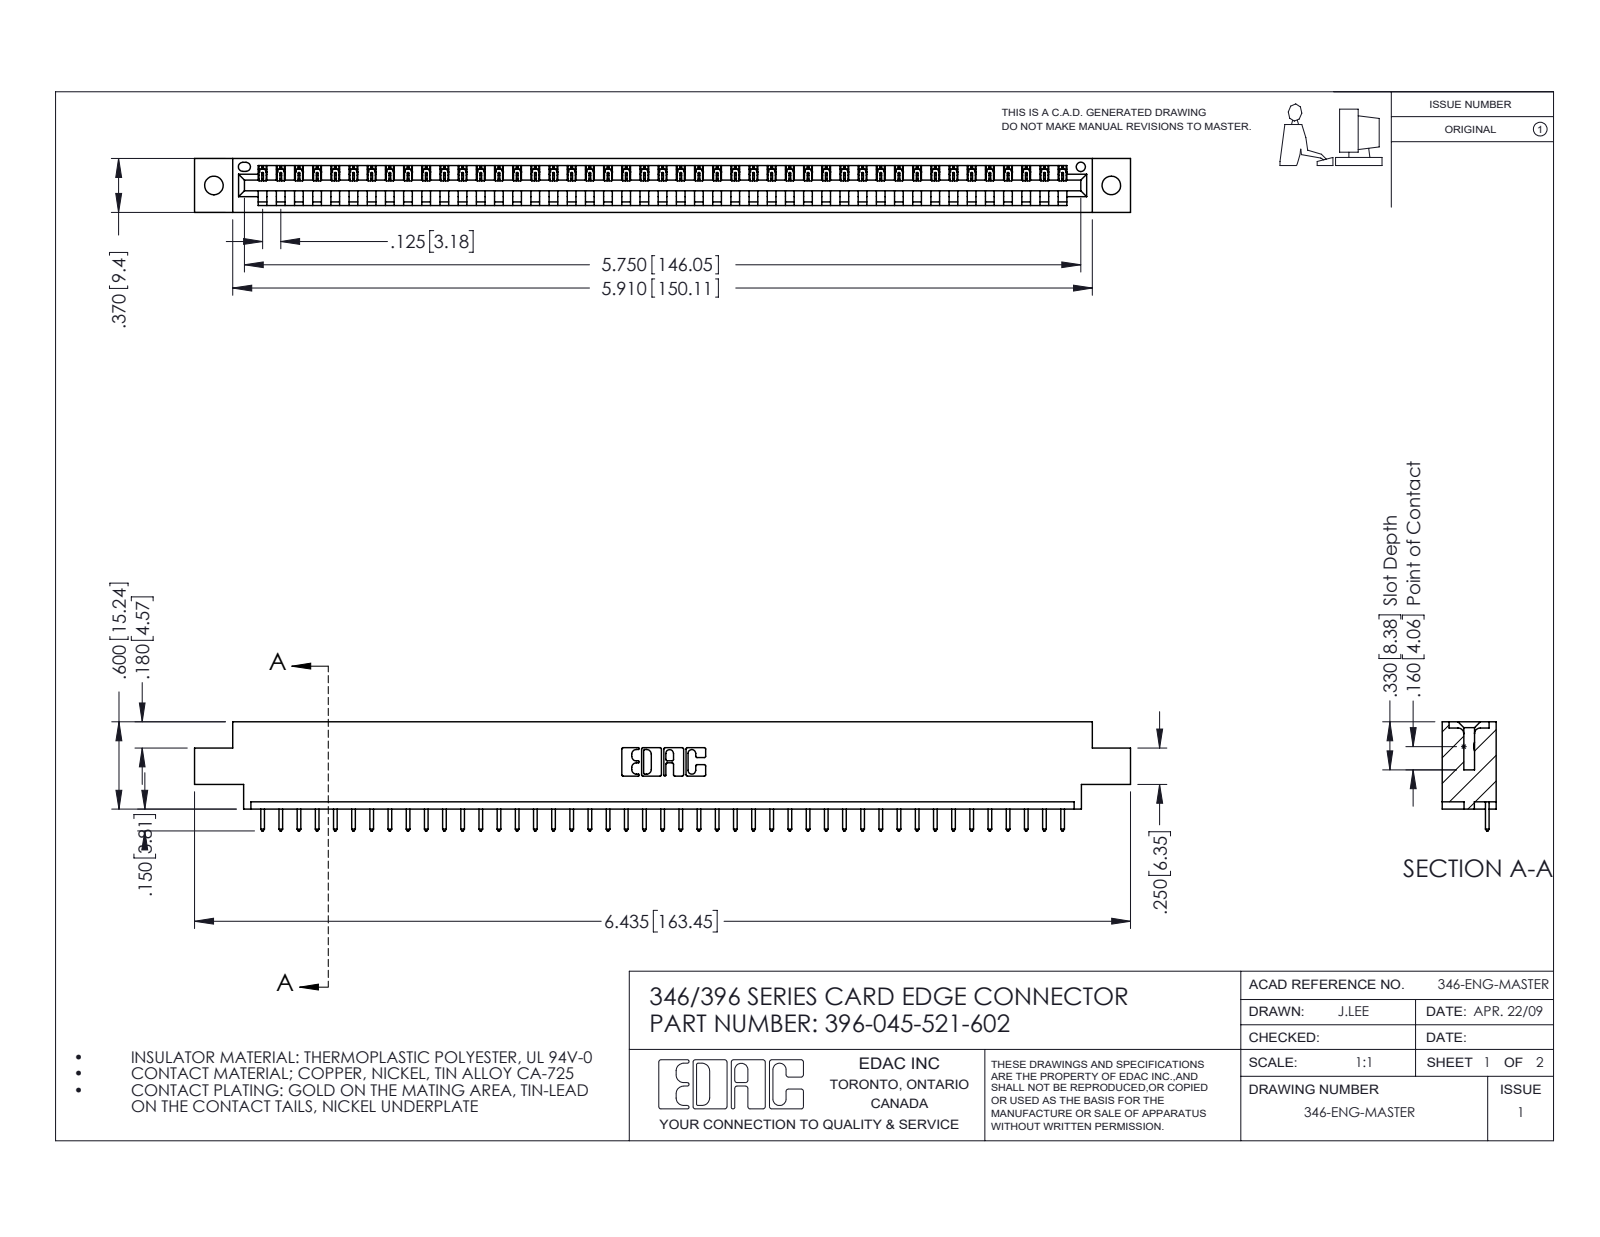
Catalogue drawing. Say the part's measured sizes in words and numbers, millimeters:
The part is named "396-045-521-602; 345-292-001_345-293-121; 346 Part_0.170 Offset - 0.128 Dia". Its 3-D file was written by "SolidWorks 2016 (CONFIG_CONTROL_DESIGN)". It is 46 solids with 2736 faces: 1880 planar, 856 cylindrical and 0 other. Overall it measures 163.4 by 19.1 by 9.4 millimeters. Its volume is 15 400 cubic millimeters and its surface area 18 590 square millimeters. Round holes: 2 of diameter 3.3, 1 of diameter 1.6. Partial cylindrical surfaces (rounded edges, fillets, slot ends): 90 of radius 0.2, 90 of radius 0.3, 22 of radius 0.3, 6 of radius 0.2, 6 of radius 0.8, 3 of radius 0.7, 2 of radius 0.8, 2 of radius 1. The main face-to-face distances are 1.2, 8.2, 9.4, 6.4, 1.8, 7.6, 0.6, 3.8, 5.6, 2.5. The hole center spacings are 6.2, 151.4, 156.7.
